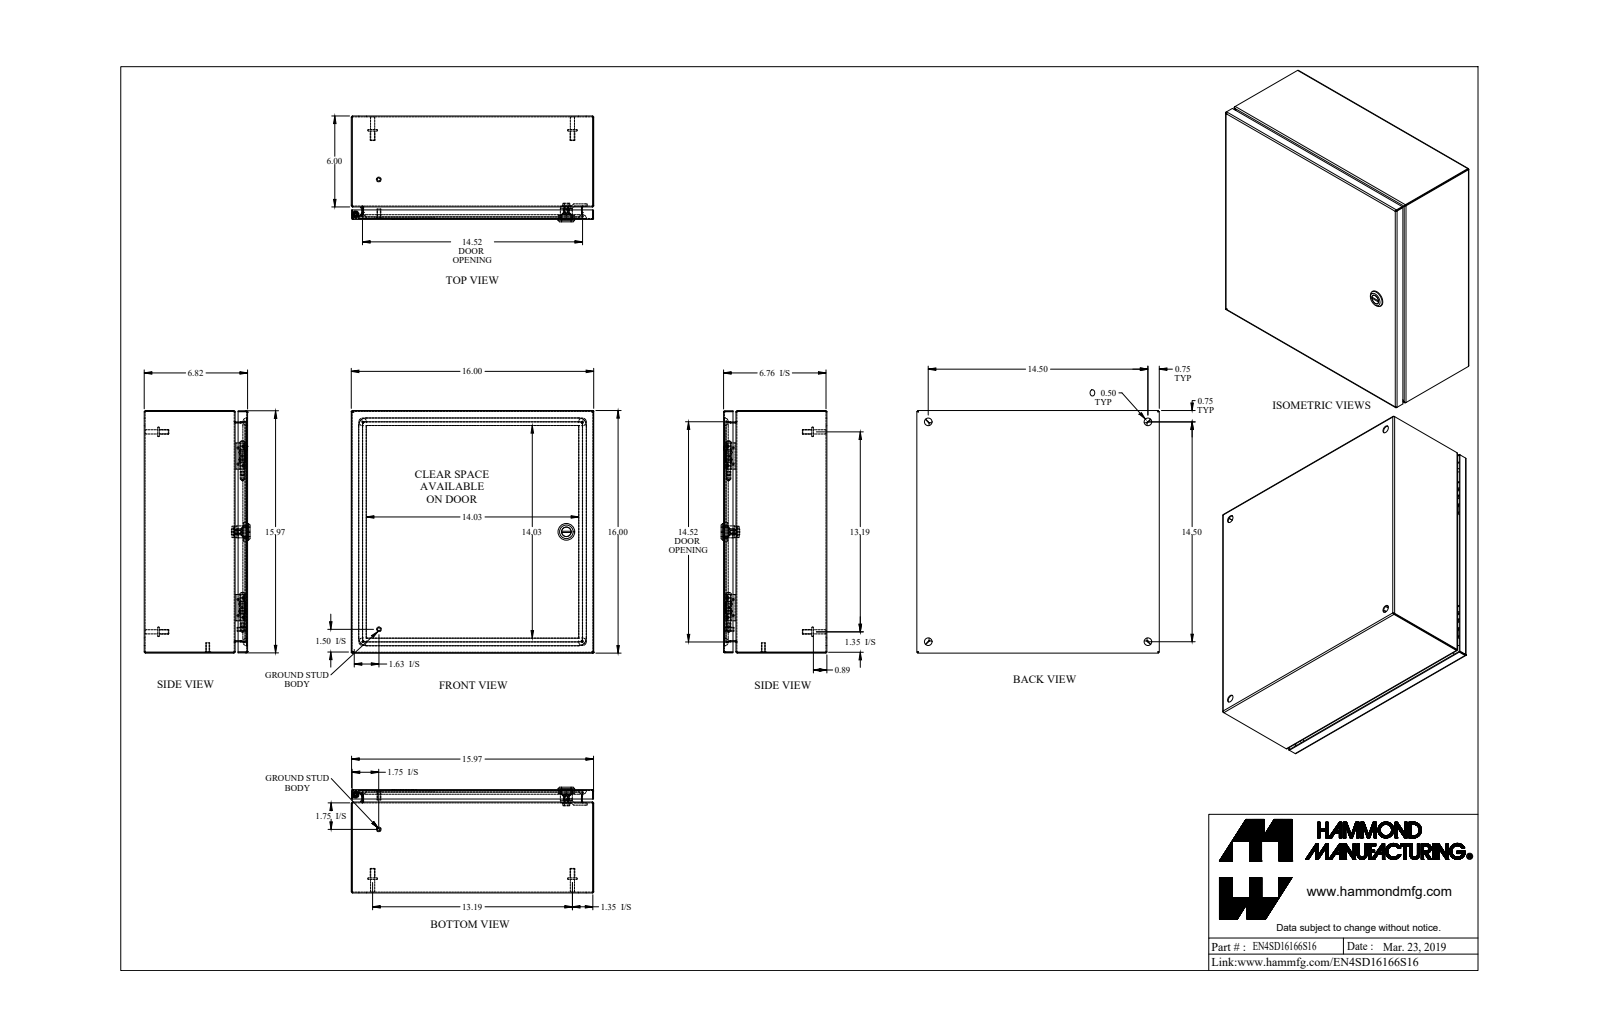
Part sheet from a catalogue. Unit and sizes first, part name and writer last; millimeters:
Units: millimetres
Overall size (bounding box): 406.4 × 406.4 × 177.3
Round holes (diameter × count): ⌀12.7 ×5, ⌀4.4 ×1, ⌀5 ×1, ⌀6.1 ×1, ⌀6.1 ×1, ⌀9.8 ×1, ⌀16 ×1, ⌀19.5 ×1
Round bosses / shafts (diameter × count): ⌀8 ×6, ⌀15.9 ×4, ⌀7 ×4, ⌀6.4 ×2, ⌀27.9 ×1, ⌀19.9 ×1, ⌀15.9 ×1, ⌀13.3 ×1
Partial cylindrical surfaces — rounded edges, fillets, slot ends (radius × count): R0.7 ×21, R2.2 ×21, R4.8 ×12, R0.2 ×4, R1.6 ×4, R6.4 ×4, R12.7 ×4, R3.2 ×2
Main face-to-face distances: 1.4, 405, 1.4, 170.4, 171.8, 171.8, 173.3, 403.5, 406.4, 151
Hole centre spacings: 368.3, 186.1, 387.9, 520.9
Volume: 1 060 000 mm³ · Surface area: 1 412 000 mm²
Bodies: 22 solids, 656 faces (303 planar, 211 cylindrical, 142 other)
Part name (STEP PRODUCT): EN4SD16166S16_Default
STEP written by: SolidWorks 2019 (CONFIG_CONTROL_DESIGN)
